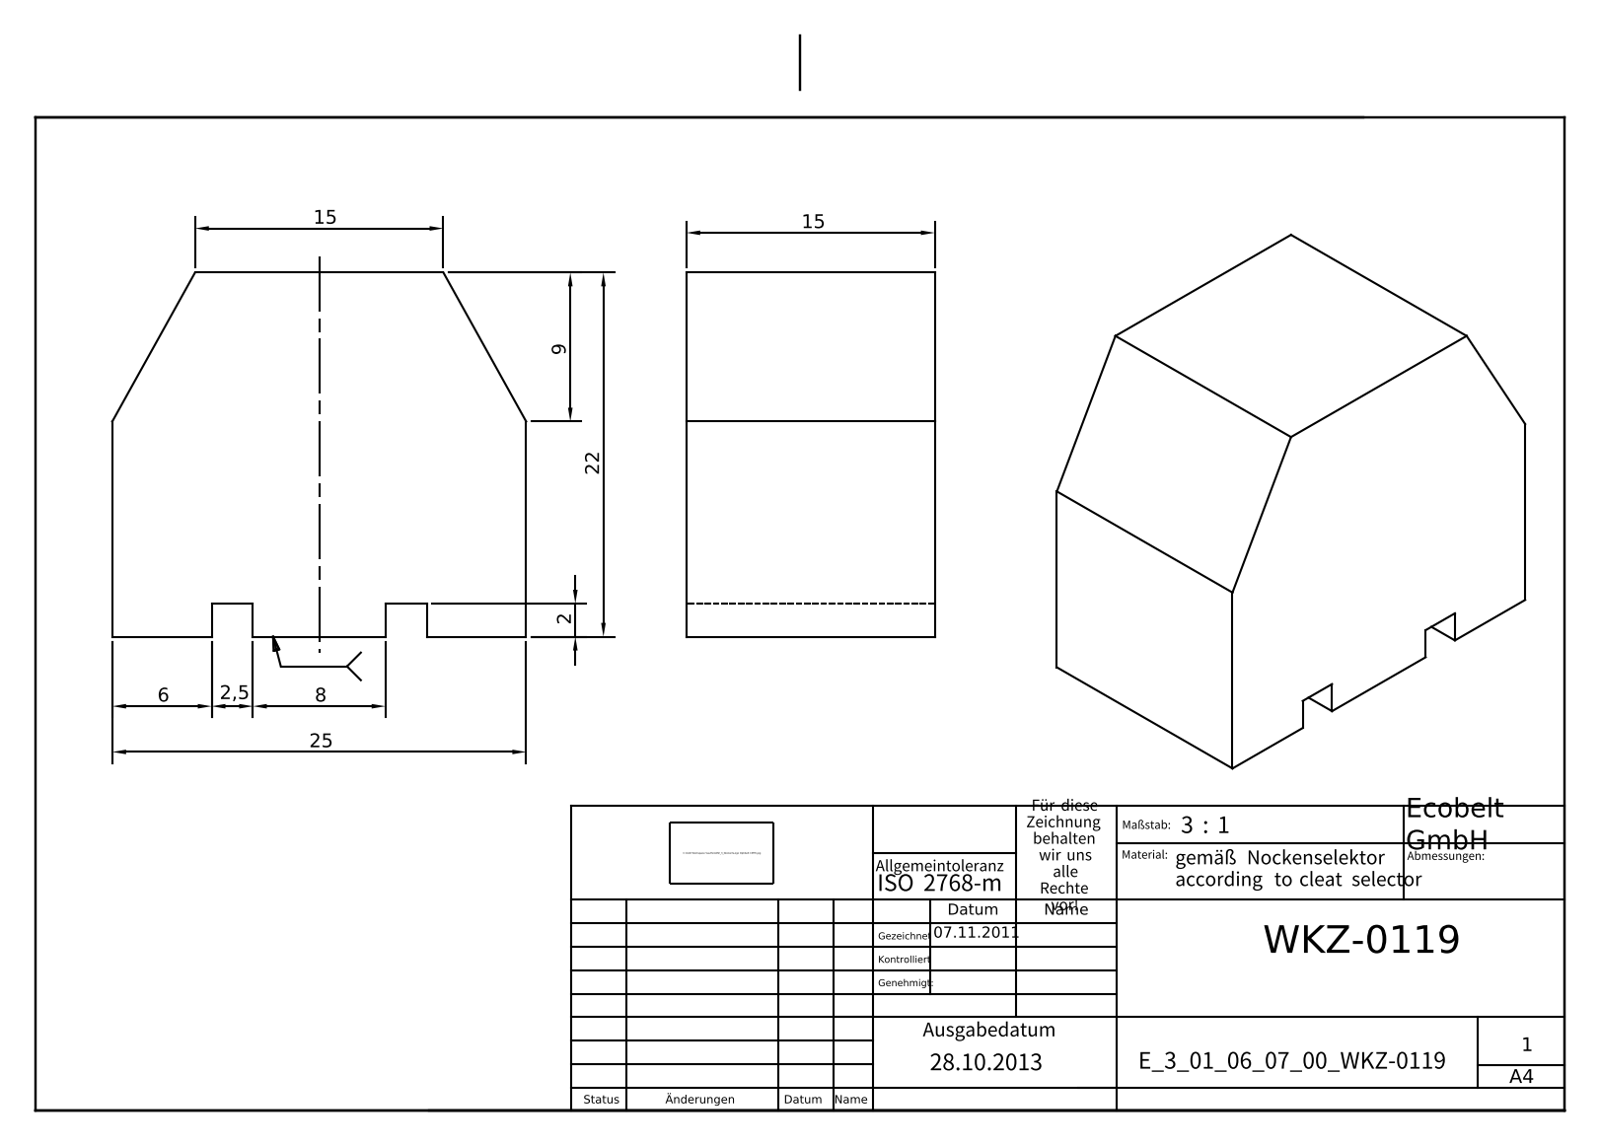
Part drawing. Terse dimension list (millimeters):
name: E_3_01_06_07_00_WKZ-0119
written by: Autodesk Inventor 2025 (AUTOMOTIVE_DESIGN)
unit: mm
bodies: 1 solid, 16 faces (16 planar, 0 cylindrical, 0 other)
size: 25 × 22 × 15
volume: 7 425 mm³; area: 2 409 mm²
face distances: 15, 22, 25, 2, 20, 6, 8.5, 16.5, 19, 2.5
